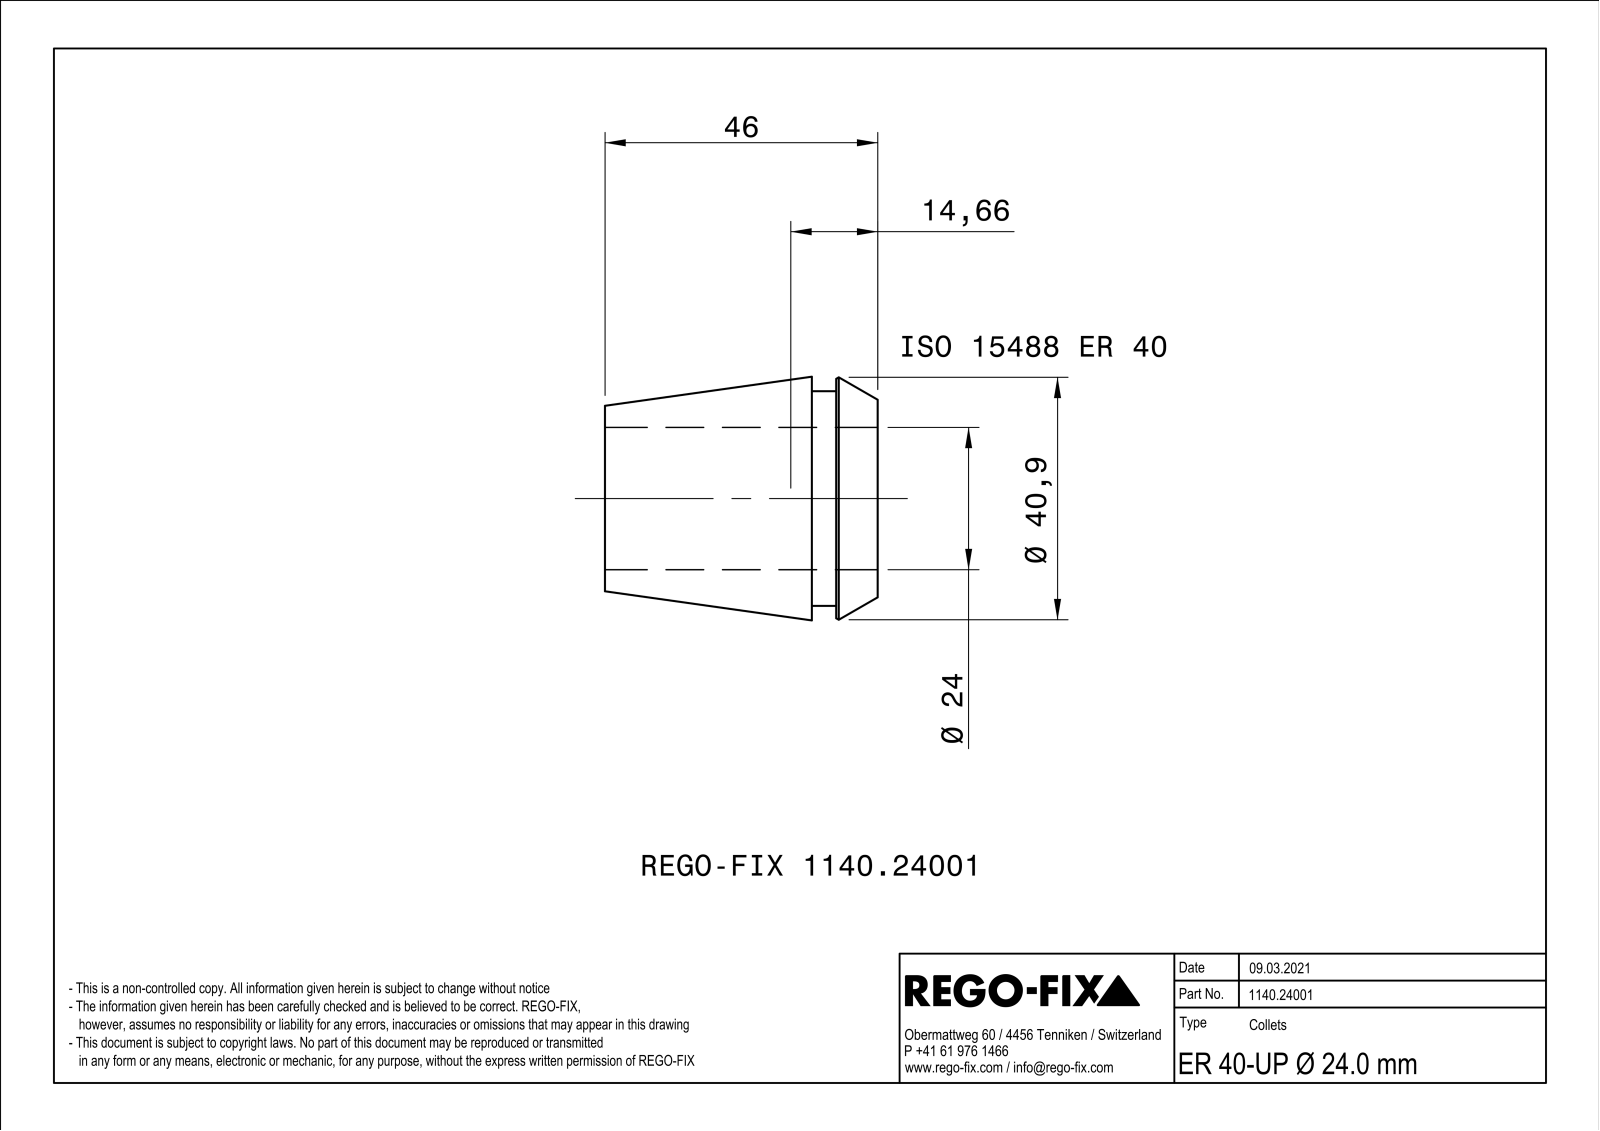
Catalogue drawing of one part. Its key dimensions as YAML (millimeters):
part_name: "NOCUT"
step_written_by: "SIEMENS PLM Software Solid Edge ST10 (AUTOMOTIVE_DESIGN)"
units: millimeters
bodies: {solids: 1, faces: 177, planar: 88, cylindrical: 9, other: 80}
overall_size: [46, 40.99, 40.99]
volume: 23004
surface_area: 16786
round_holes:
  - {diameter: 24, count: 1}
round_bosses_or_shafts:
  - {diameter: 36.2, count: 1}
face_to_face_distances: [1, 11.1, 46, 34.9, 7, 4.1, 39, 7.5, 0.5, 3.6]
